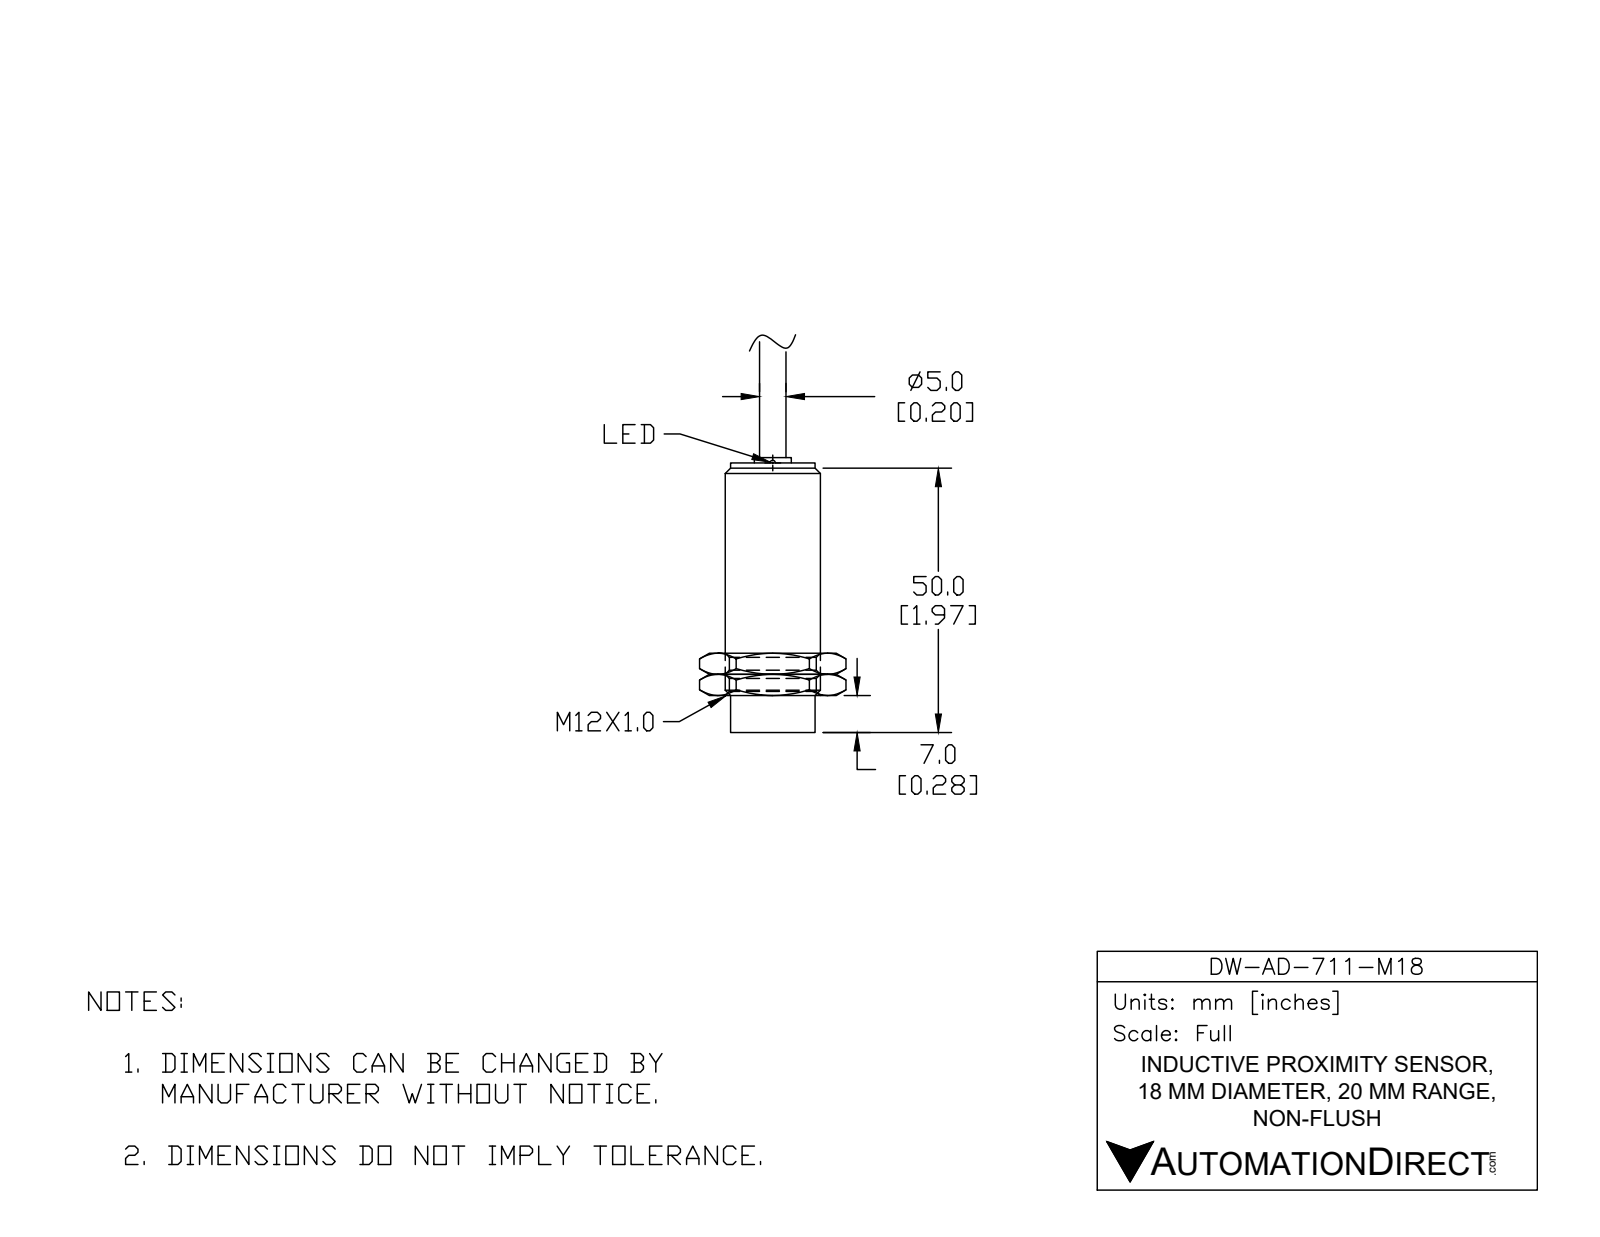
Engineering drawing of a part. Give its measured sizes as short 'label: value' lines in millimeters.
name: DW-AD-711-M18
written by: SolidWorks 2017 (AUTOMOTIVE_DESIGN)
unit: mm
bodies: 2 solids, 37 faces (18 planar, 7 cylindrical, 12 other)
size: 76.6 × 18 × 18
volume: 13 300 mm³; area: 3 818 mm²
bosses: 1× ⌀18, 1× ⌀16.4, 1× ⌀10.5, 1× ⌀6.8, 1× ⌀5, 1× ⌀3
face distances: 51, 0.8, 53, 2, 51.8, 1.2, 48, 3, 3.8, 5
